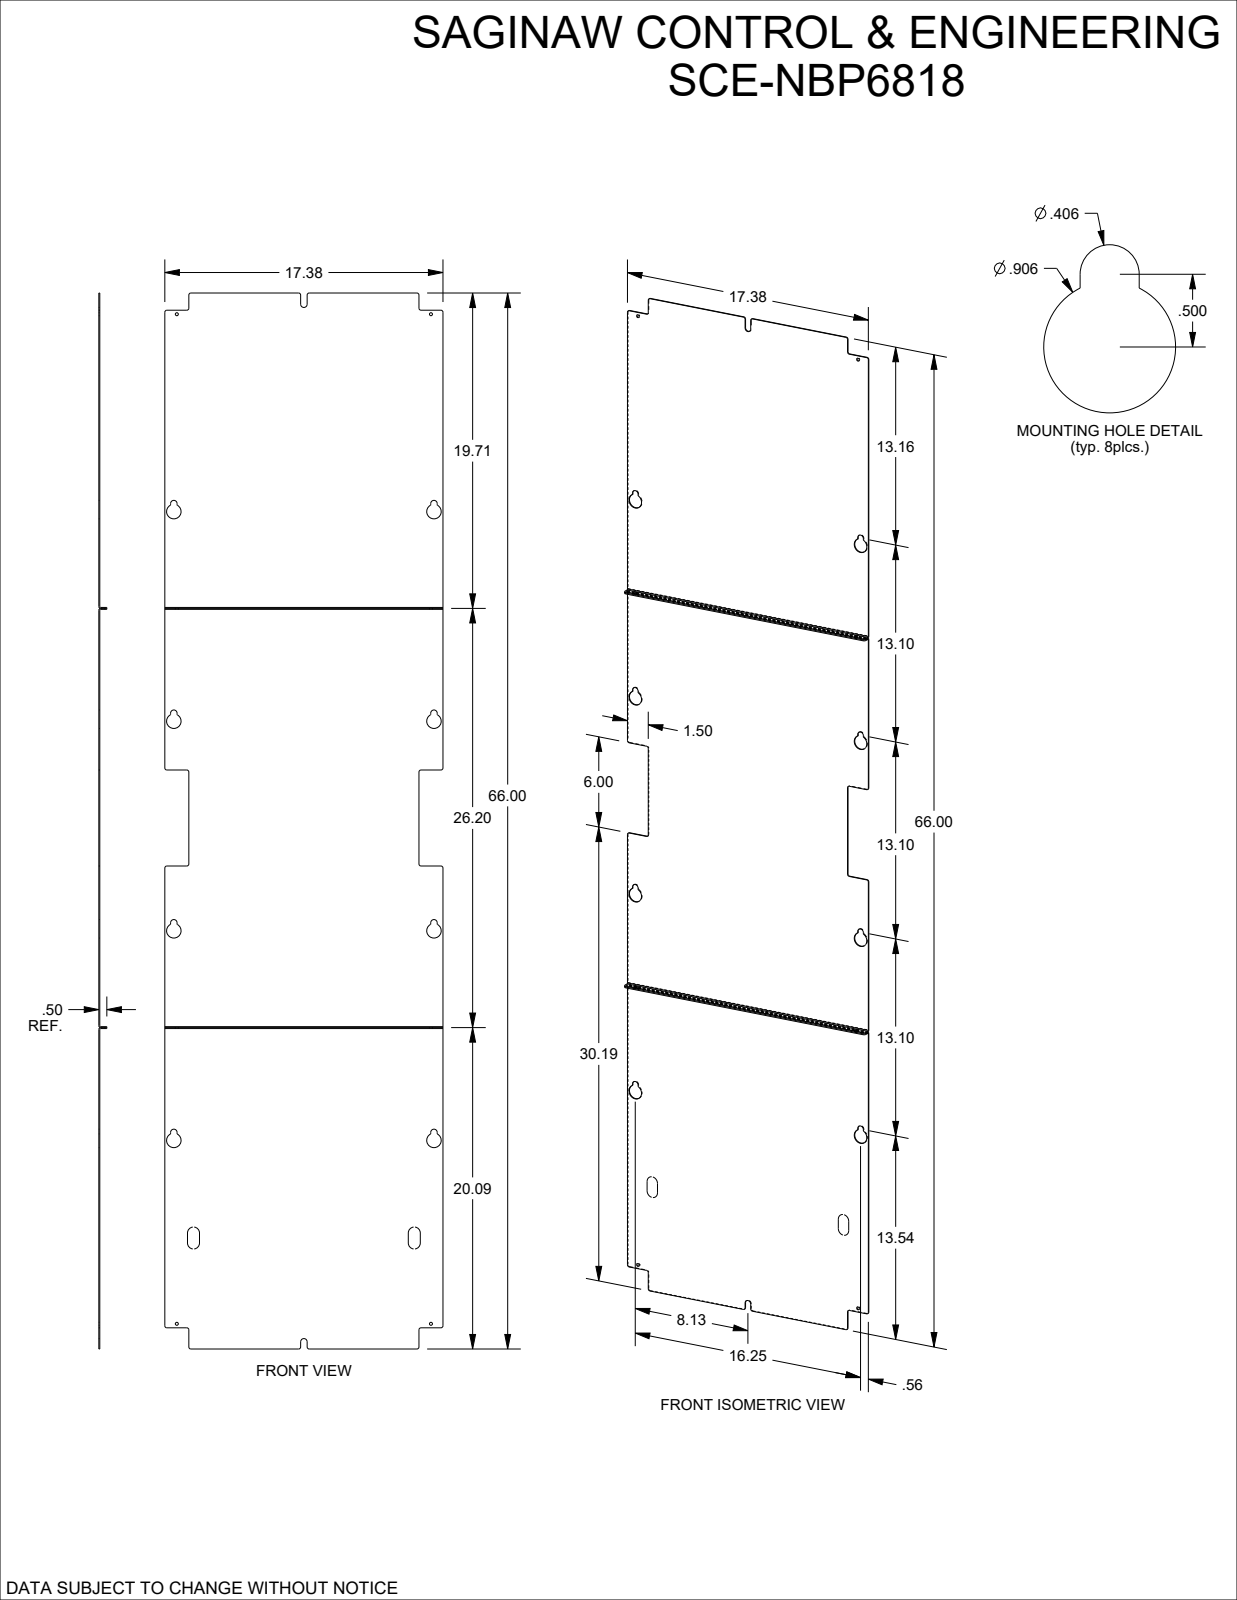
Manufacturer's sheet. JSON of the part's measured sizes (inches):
{"part_name": "SCE-NBP6818", "step_written_by": "SolidWorks 2023 (AUTOMOTIVE_DESIGN)", "units": "inches", "bodies": {"solids": 3, "faces": 174, "planar": 80, "cylindrical": 94, "other": 0}, "overall_size": [66, 17.375, 0.5], "volume_in3": 68.57, "surface_area_in2": 2302, "round_holes": [[0.906, 8], [0.188, 6]], "partial_cylinders_radius": [[0.125, 26], [0.03, 12], [0.203, 10], [0.052, 4], [0.112, 4]], "face_to_face_distances": [0.06, 26.2, 0.12, 0.06, 26.26, 26.32, 26.26, 26.14, 26.14, 26.08], "hole_center_spacings": [13.1, 20.873, 16.25, 26.2, 30.83, 15.875, 11.465, 12.339]}
